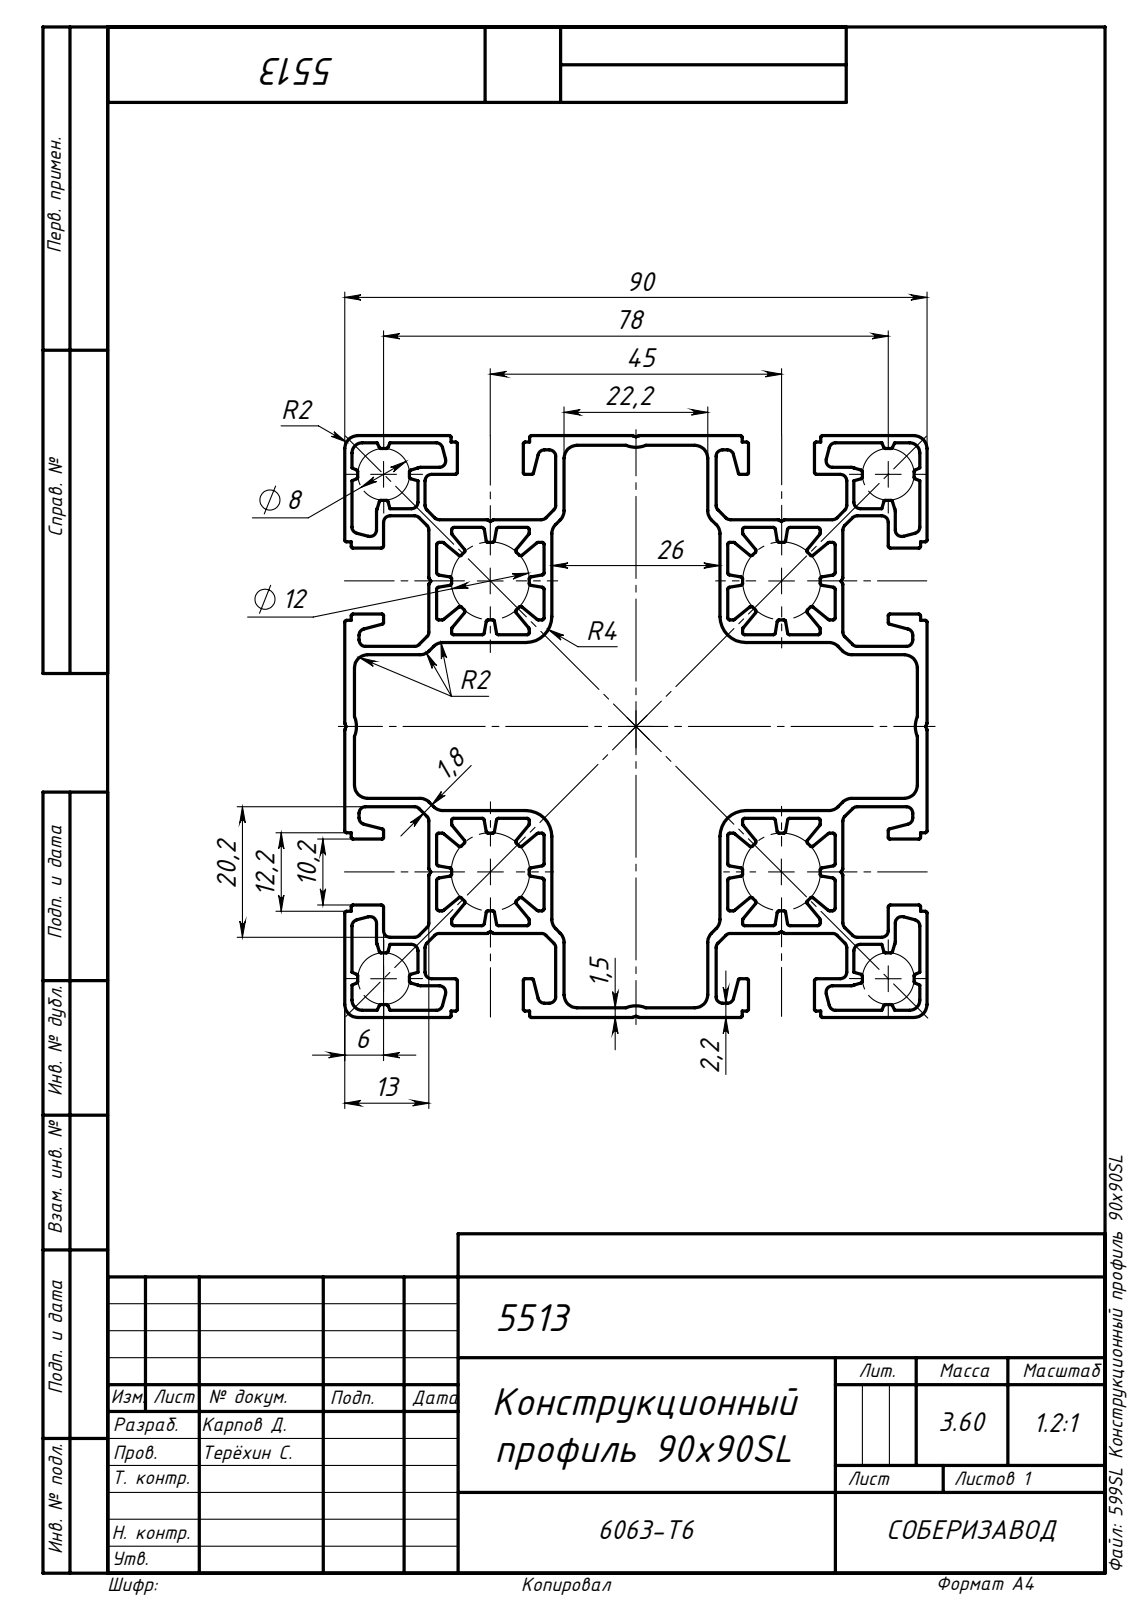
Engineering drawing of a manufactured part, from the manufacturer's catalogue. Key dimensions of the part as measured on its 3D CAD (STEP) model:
STEP written by: SolidWorks 2019 (AUTOMOTIVE_DESIGN)
Units: millimetres
Bodies: 1 solid, 862 faces (450 planar, 412 cylindrical, 0 other)
Overall size (bounding box): 1000 × 90 × 90
Volume: 1 332 000 mm³ · Surface area: 1 715 000 mm²
Partial cylindrical surfaces — rounded edges, fillets, slot ends (radius × count): R0.25 ×120, R0.3 ×120, R1 ×92, R2 ×28, R0.4 ×24, R0.35 ×8, R4 ×8, R1.6 ×4
Main face-to-face distances: 45, 1.2, 17.8, 90, 13, 77, 32, 58, 19, 26.6
